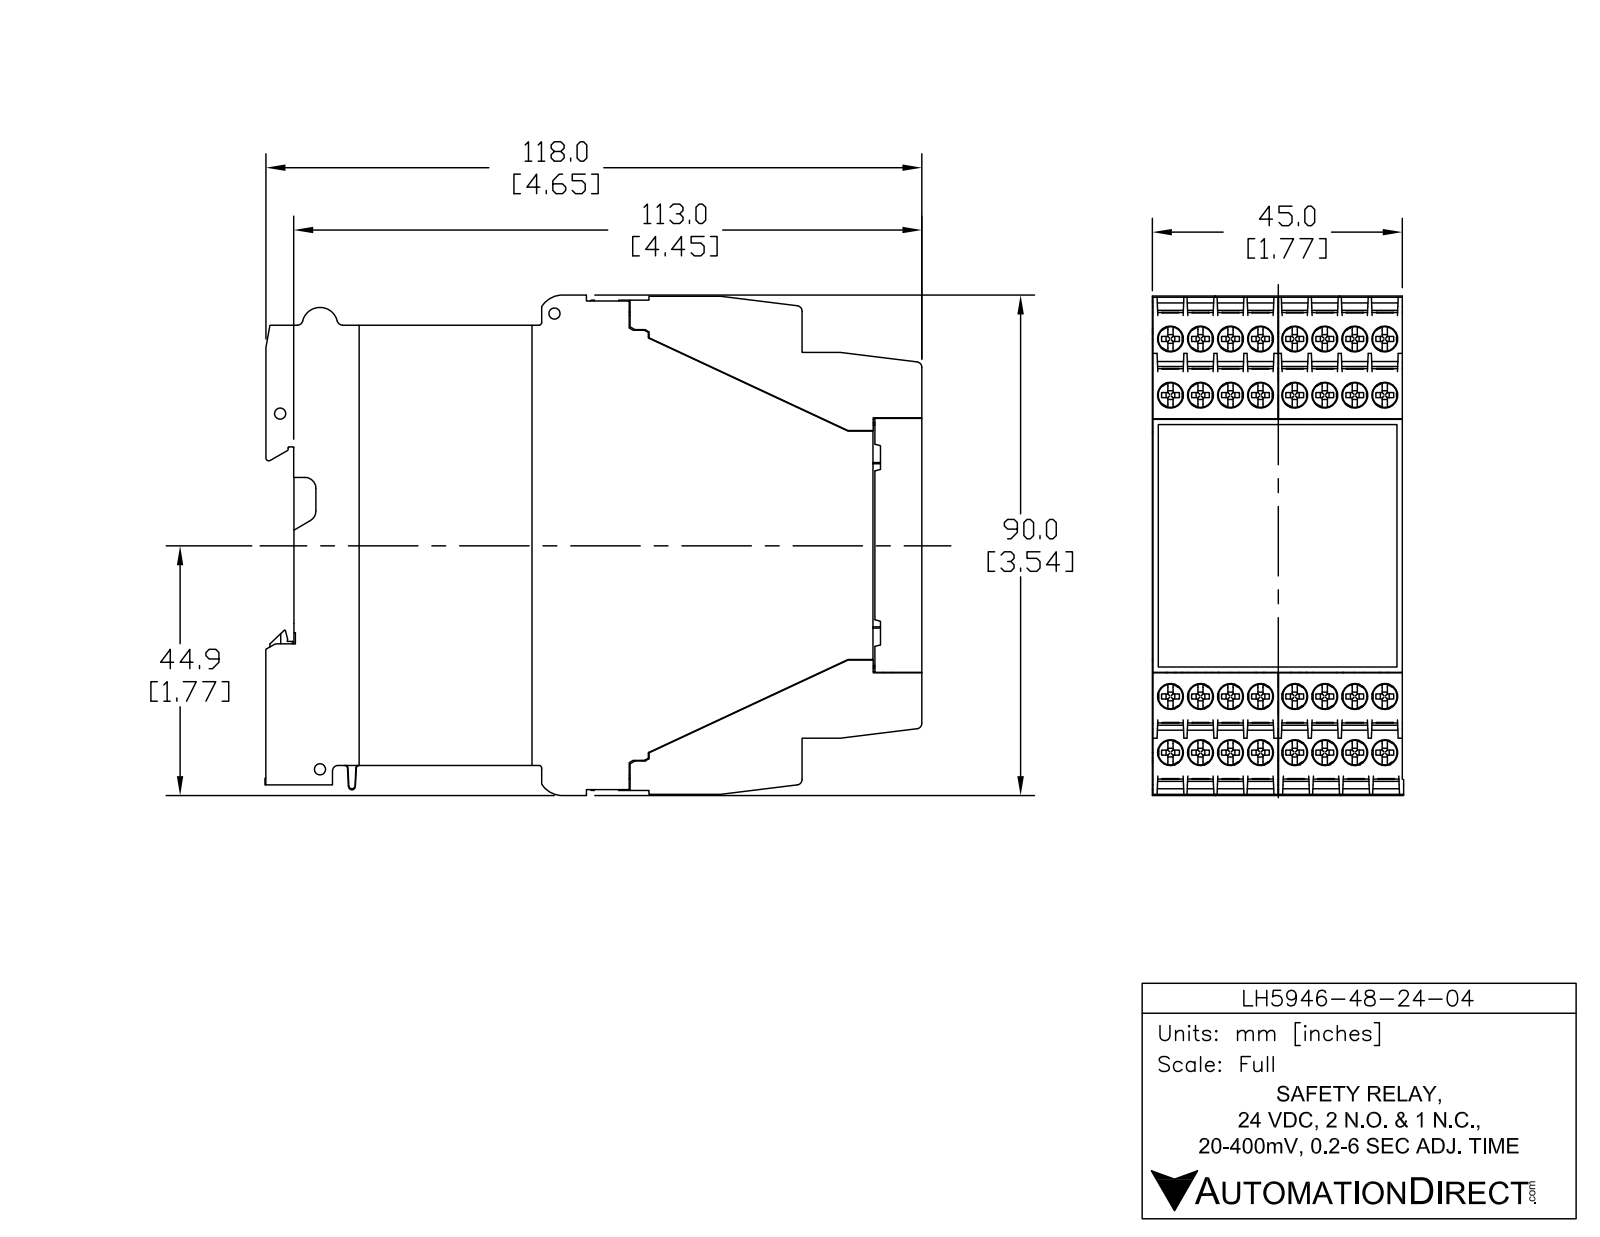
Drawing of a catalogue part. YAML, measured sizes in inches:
part_name: "LH5946-48-115-04"
step_written_by: "SolidWorks 2017 (AUTOMOTIVE_DESIGN)"
units: inches
bodies: {solids: 1, faces: 3585, planar: 2713, cylindrical: 591, other: 281}
overall_size: [4.654, 3.537, 1.791]
volume: 24.89
surface_area: 89.21
round_holes:
  - {diameter: 0.181, count: 32}
  - {diameter: 0.12, count: 8}
  - {diameter: 0.079, count: 3}
  - {diameter: 0.067, count: 2}
  - {diameter: 0.079, count: 2}
  - {diameter: 0.157, count: 2}
round_bosses_or_shafts:
  - {diameter: 0.173, count: 32}
  - {diameter: 0.109, count: 4}
  - {diameter: 0.109, count: 4}
  - {diameter: 0.079, count: 2}
  - {diameter: 0.087, count: 1}
partial_cylinders:
  - {radius: 0.012, count: 96}
  - {radius: 0.008, count: 48}
  - {radius: 0.039, count: 43}
  - {radius: 0.02, count: 25}
  - {radius: 0.024, count: 14}
  - {radius: 0.055, count: 4}
  - {radius: 0.006, count: 3}
  - {radius: 0.014, count: 3}
face_to_face_distances: [1.791, 1.787, 4.449, 0.035, 0.031, 1.756, 3.11, 0.028, 1.783, 0.383]
hole_center_spacings: [0.213, 0.451, 2.541, 0.886, 0.398, 0.425, 0.582, 0.971]
